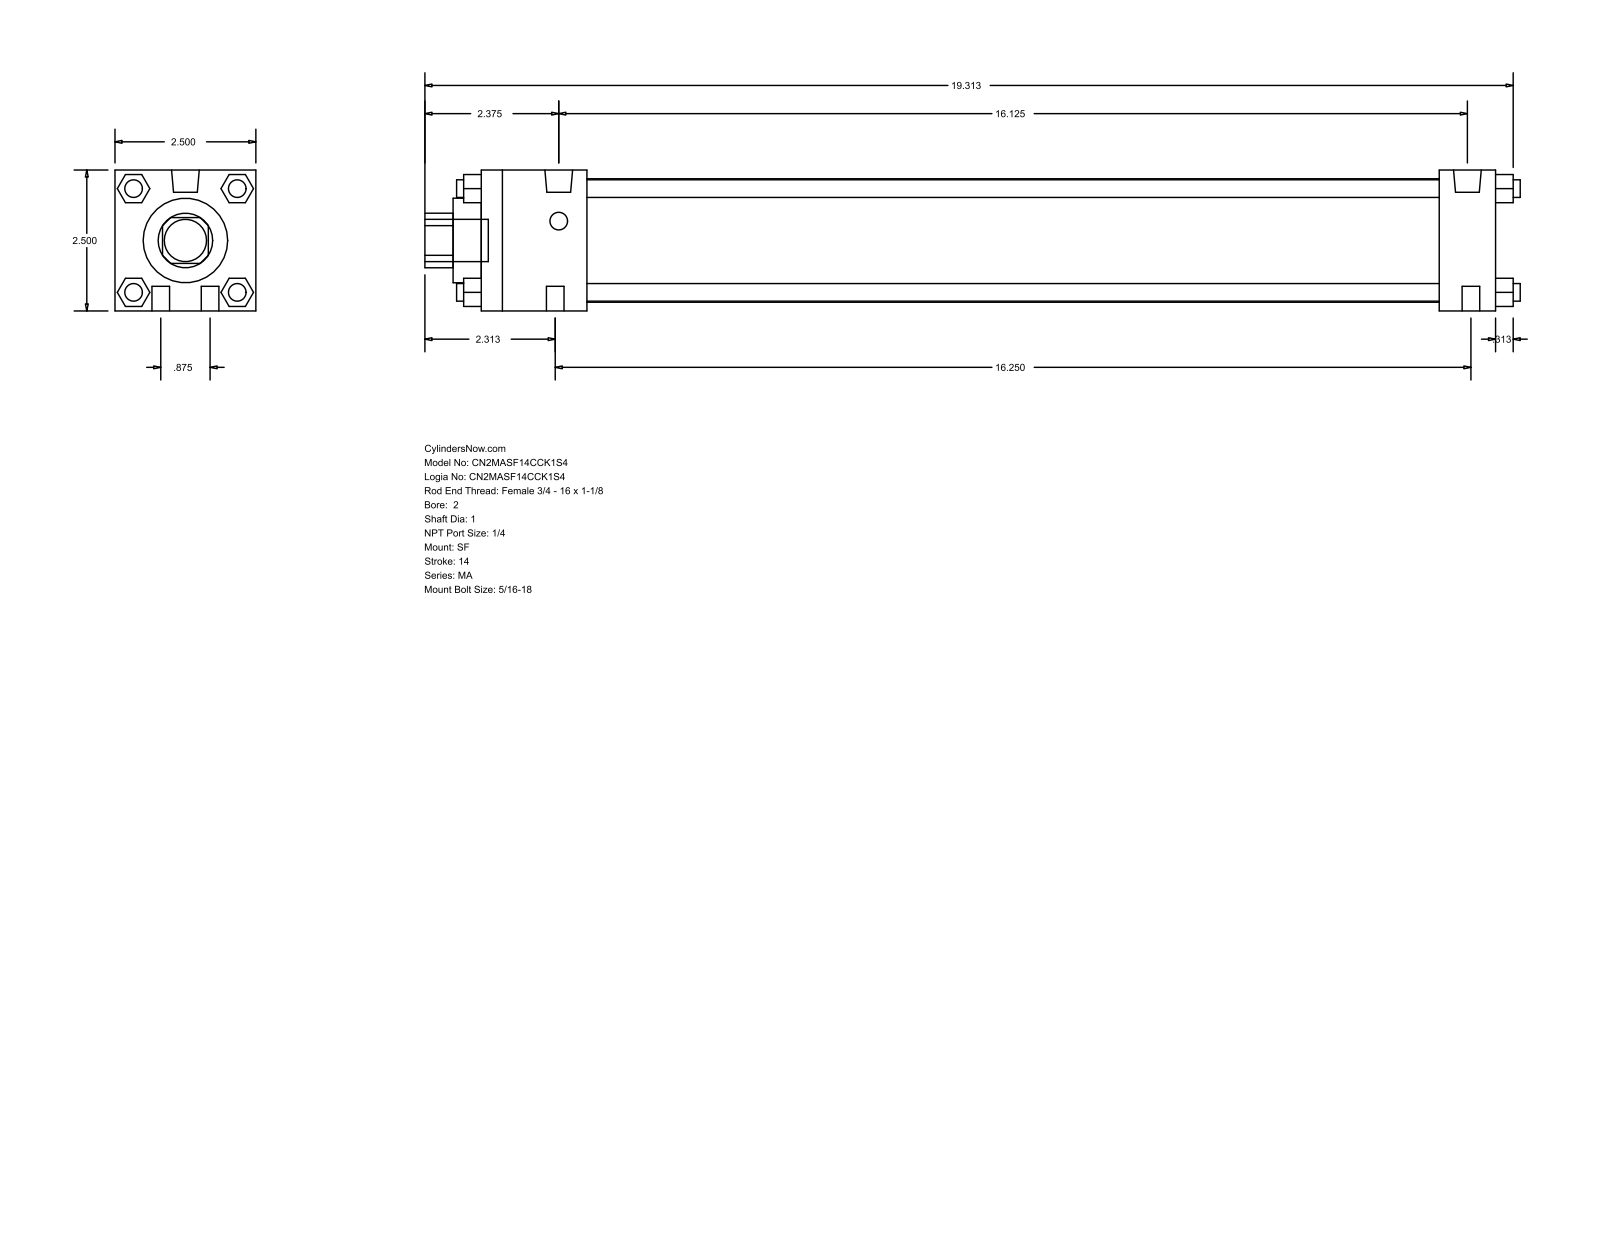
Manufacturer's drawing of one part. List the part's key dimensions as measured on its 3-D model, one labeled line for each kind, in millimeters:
Part name (STEP PRODUCT): MA_SF__0200_1
STEP written by: GSSL Pune (CONFIG_CONTROL_DESIGN)
Units: millimetres
Bodies: 0 solids, 124 faces (94 planar, 30 cylindrical, 0 other)
Overall size (bounding box): 493.71 × 63.5 × 63.5
Round holes (diameter × count): ⌀25.4 ×1, ⌀38.1 ×1, ⌀55.63 ×1
Round bosses / shafts (diameter × count): ⌀7.94 ×10, ⌀12.49 ×2, ⌀19.05 ×1
Partial cylindrical surfaces — rounded edges, fillets, slot ends (radius × count): R12.29 ×1
Main face-to-face distances: 63.5, 457.2, 12.7, 25.4, 431.8, 47.63, 384.17, 409.57, 40.47, 23.37
